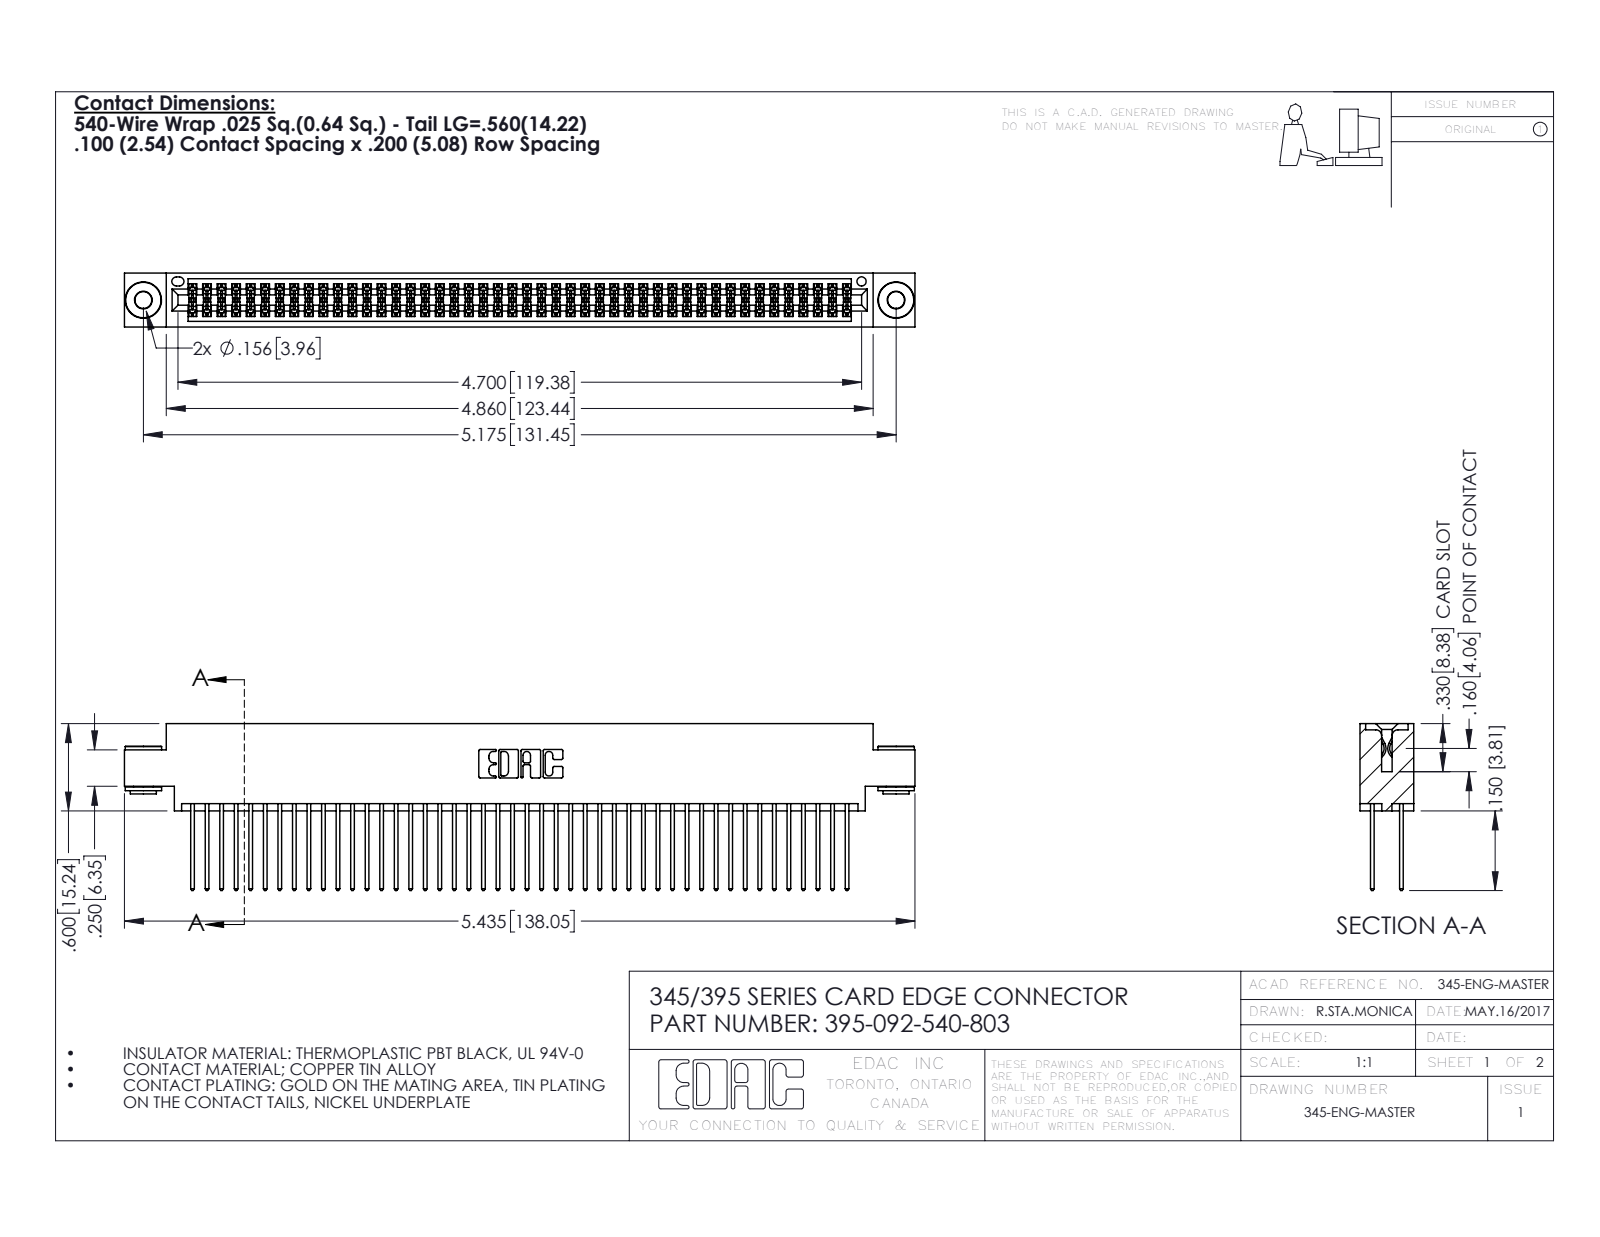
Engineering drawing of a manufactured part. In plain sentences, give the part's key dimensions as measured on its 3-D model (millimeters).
The part is named "395-092-540-803; 345 Part_0.170 Offset - 0.156 Dia-TH; 345-250-002_345-250-002-102; 345-292-001_345-293-140". Its 3-D file was written by "SolidWorks 2016 (CONFIG_CONTROL_DESIGN)". It is 95 solids with 4768 faces: 3130 planar, 1630 cylindrical and 8 other. Overall it measures 138 by 29.1 by 9.4 millimeters. Its volume is 13 700 cubic millimeters and its surface area 22 300 square millimeters. Round holes: 2 of diameter 2.9, 2 of diameter 4, 1 of diameter 1.6. Round bosses or shafts: 2 of diameter 6.4, 2 of diameter 4.6, 2 of diameter 3.5. Partial cylindrical surfaces (rounded edges, fillets, slot ends): 138 of radius 0.2, 92 of radius 0.3, 22 of radius 0.3, 6 of radius 0.2, 6 of radius 0.8, 3 of radius 0.7, 2 of radius 0.4, 2 of radius 0.5. The main face-to-face distances are 1.8, 7.6, 5.1, 2.5, 6.9, 0.6, 9.4, 5.7, 4.4, 3.8. The hole center spacings are 6.9, 125.5, 131.4.
